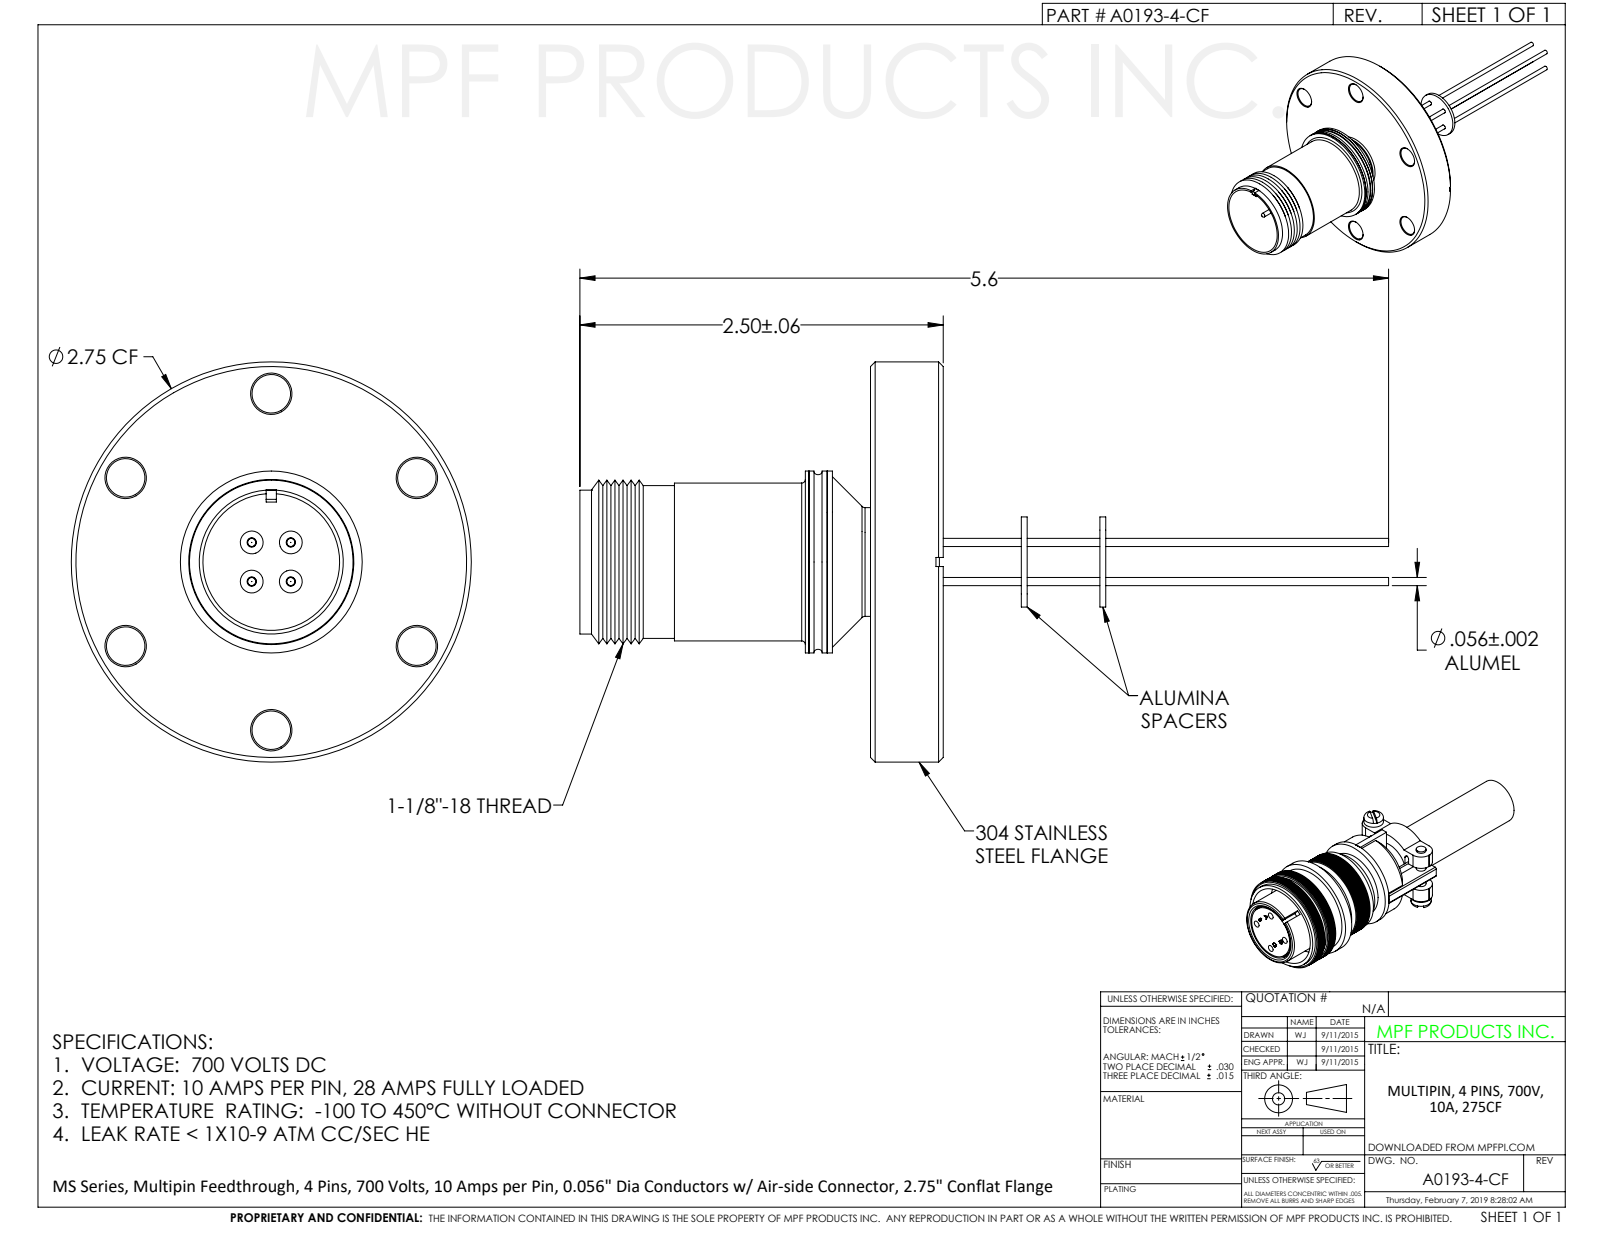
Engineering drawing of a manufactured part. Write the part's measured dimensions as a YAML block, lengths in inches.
part_name: "A0193-4-CF"
step_written_by: "SolidWorks 2012 (CONFIG_CONTROL_DESIGN)"
units: inches
bodies: {solids: 1, faces: 217, planar: 56, cylindrical: 106, other: 55}
overall_size: [5.595, 2.75, 2.75]
volume: 3.068
surface_area: 43.54
round_holes:
  - {diameter: 0.265, count: 6}
  - {diameter: 0.675, count: 1}
  - {diameter: 0.94, count: 1}
  - {diameter: 0.96, count: 1}
  - {diameter: 0.97, count: 1}
  - {diameter: 1.035, count: 1}
  - {diameter: 1.65, count: 1}
  - {diameter: 1.902, count: 1}
round_bosses_or_shafts:
  - {diameter: 0.187, count: 4}
  - {diameter: 0.167, count: 4}
  - {diameter: 0.056, count: 4}
  - {diameter: 2.75, count: 1}
  - {diameter: 1.25, count: 1}
  - {diameter: 1.085, count: 1}
  - {diameter: 1.05, count: 1}
  - {diameter: 1.02, count: 1}
partial_cylinders:
  - {radius: 1.655, count: 2}
face_to_face_distances: [0.5, 0.449, 0.051, 0.856, 1.305, 1.356, 0.05, 0.806, 1.255, 1.306]
hole_center_spacings: [1.156, 2.002, 2.002, 2.312, 2.312]
